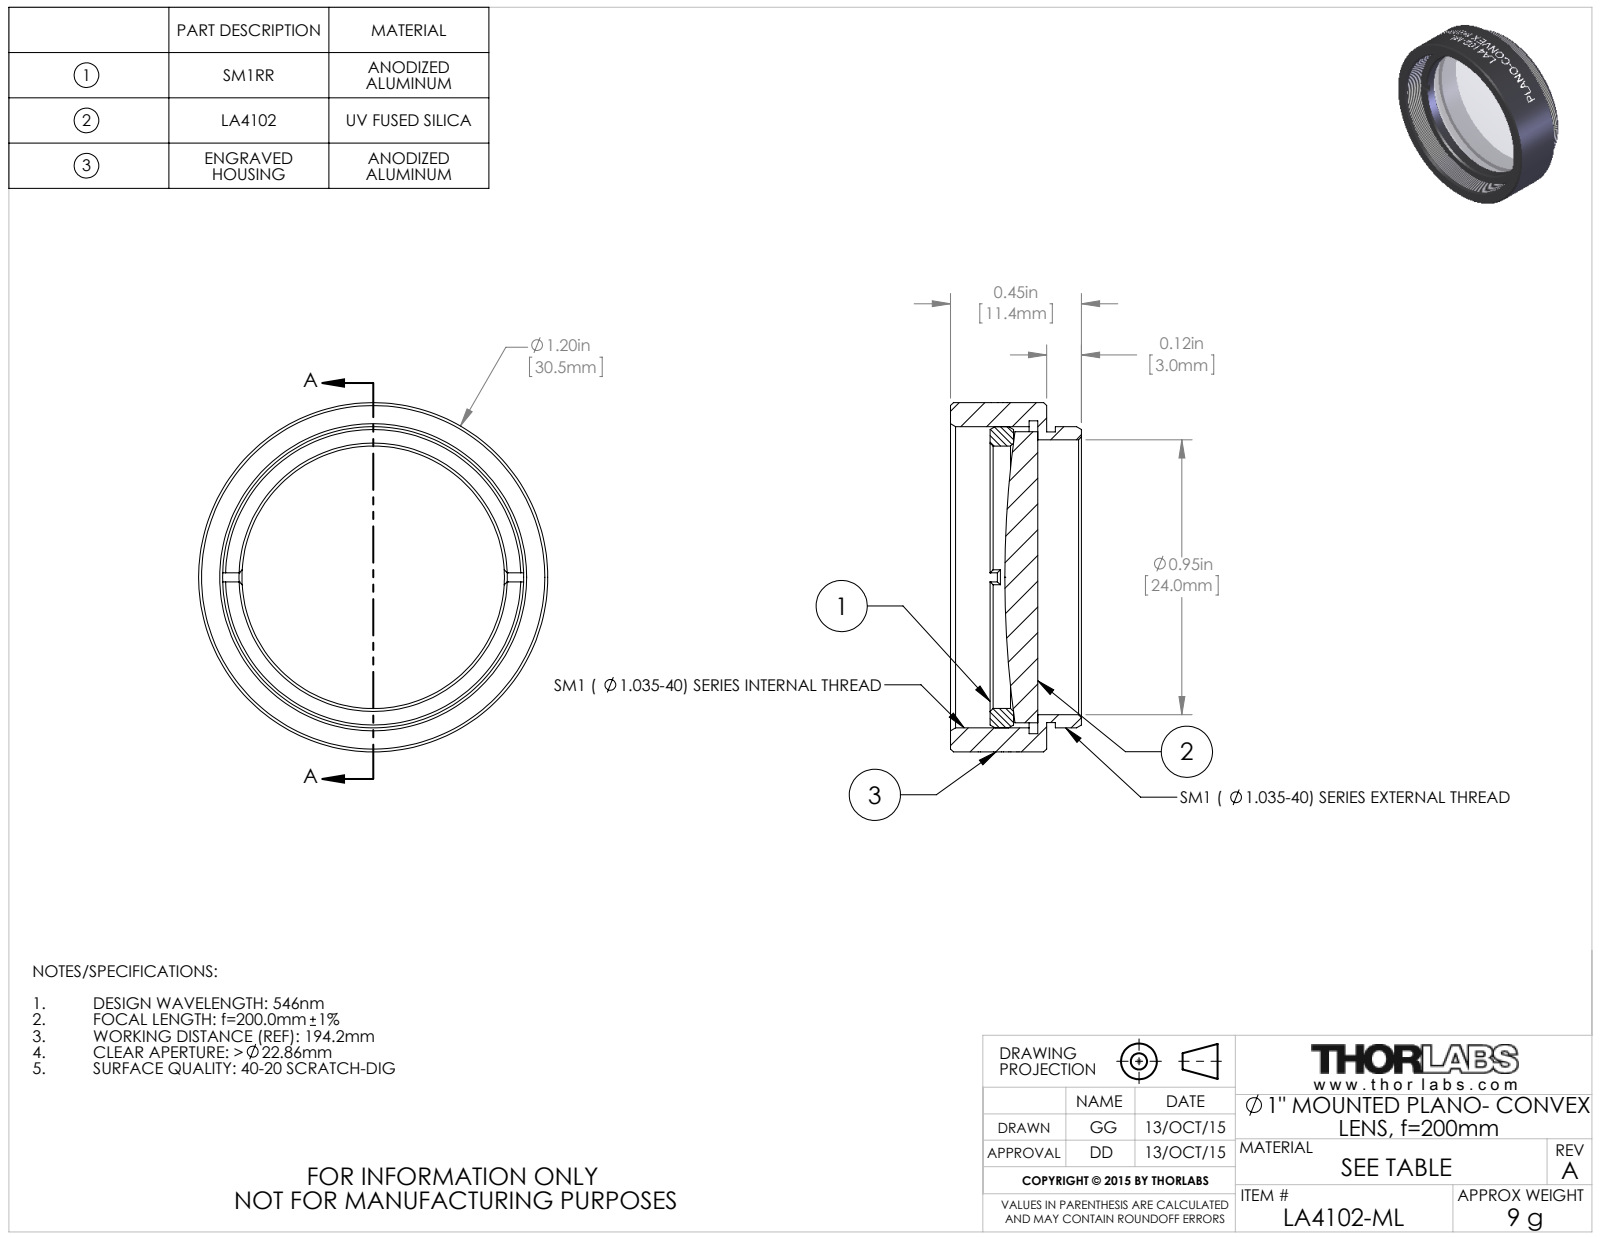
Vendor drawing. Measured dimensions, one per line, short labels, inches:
name: TTN039141-E0W
written by: SolidWorks 2014 (CONFIG_CONTROL_DESIGN)
unit: in
bodies: 3 solids, 117 faces (20 planar, 73 cylindrical, 24 other)
size: 1.2 × 1.2 × 0.45
volume: 0.202 in³; area: 6.688 in²
holes: 1× ⌀0.902, 1× ⌀0.945, 1× ⌀1.035, 1× ⌀1.075
bosses: 1× ⌀1.2, 1× ⌀1.035, 1× ⌀1, 1× ⌀0.999
face distances: 0.03, 0.33, 0.3, 0.114, 0.084, 0.216, 0.194, 0.164, 0.08, 0.136
